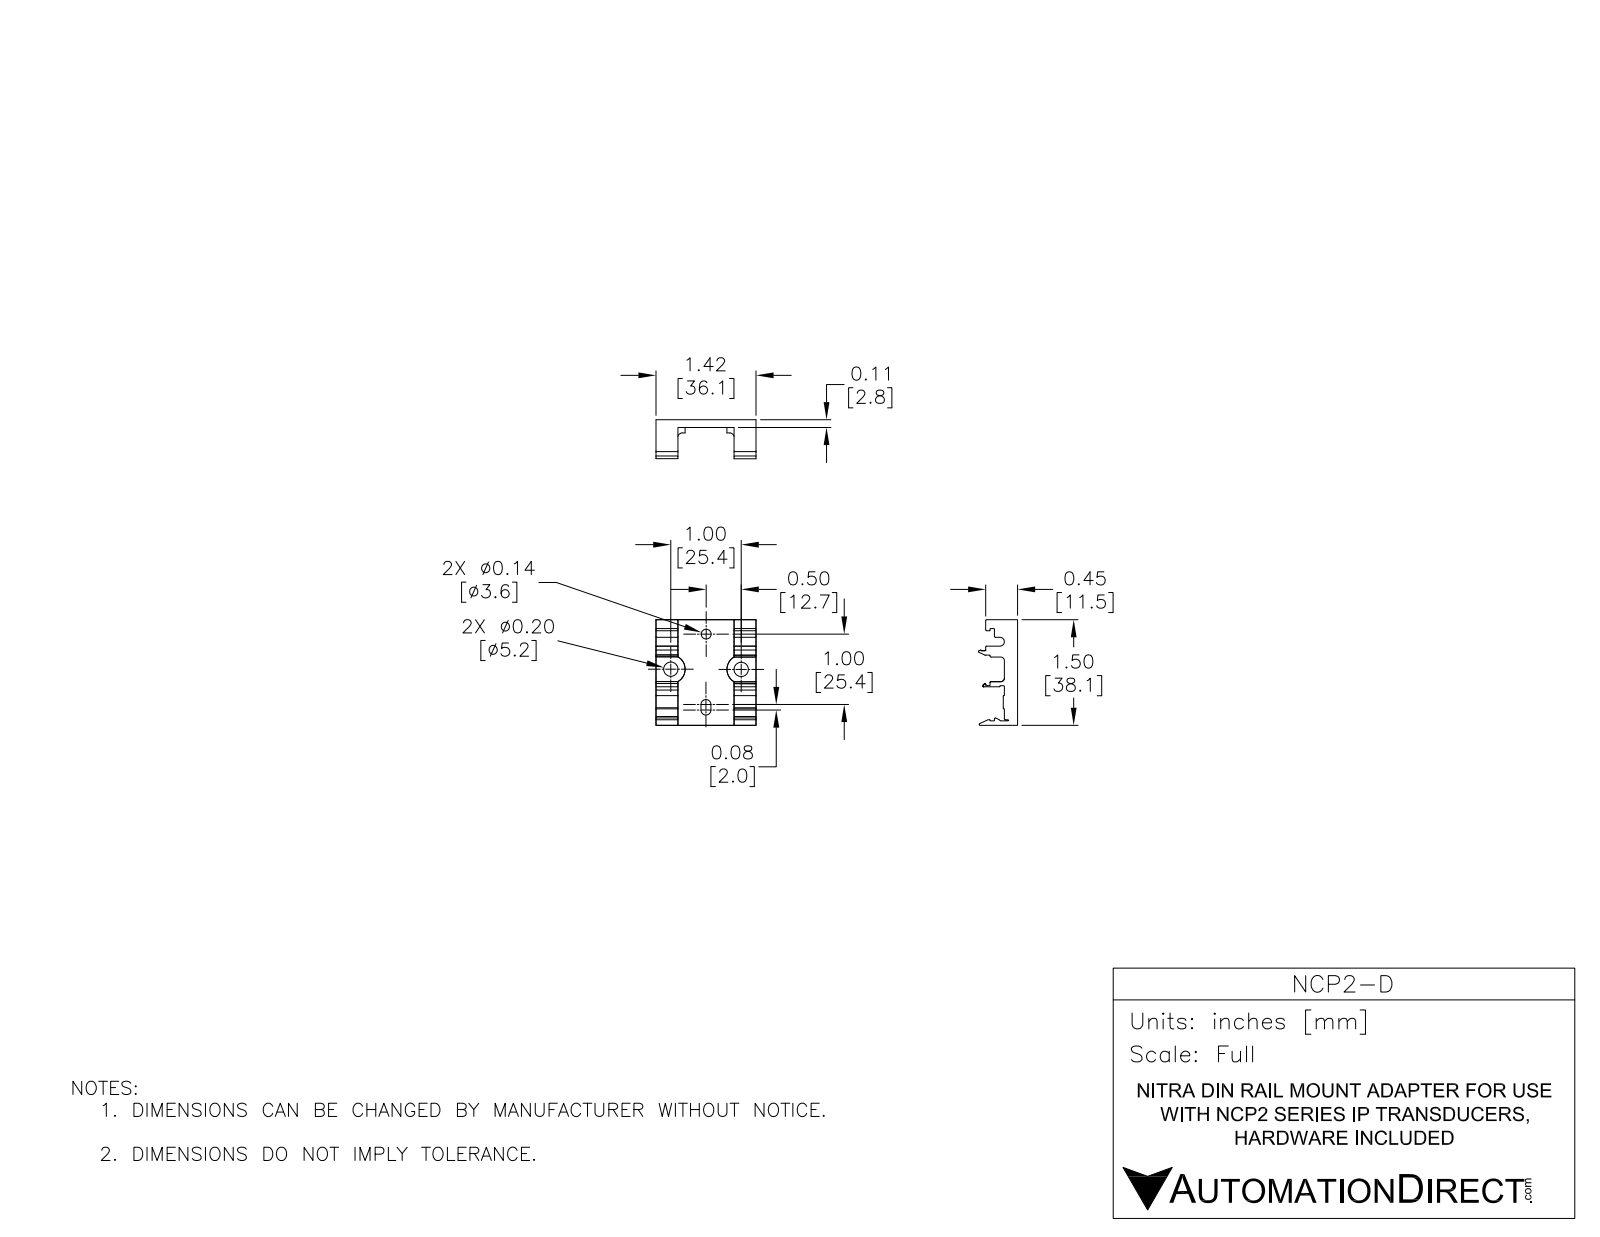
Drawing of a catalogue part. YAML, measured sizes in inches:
part_name: "NCP2-D"
step_written_by: "SolidWorks 2016 (AUTOMOTIVE_DESIGN)"
units: inches
bodies: {solids: 1, faces: 187, planar: 90, cylindrical: 95, other: 2}
overall_size: [1.5, 1.422, 0.555]
volume: 0.382
surface_area: 7.861
round_holes:
  - {diameter: 0.203, count: 2}
  - {diameter: 0.141, count: 1}
partial_cylinders:
  - {radius: 0.007, count: 17}
  - {radius: 0.012, count: 10}
  - {radius: 0.013, count: 10}
  - {radius: 0.05, count: 4}
  - {radius: 0.07, count: 2}
  - {radius: 0.203, count: 2}
  - {radius: 0.062, count: 1}
face_to_face_distances: [0.109, 0.313, 1.109, 1.422, 1.5, 0.187, 0.078, 0.797, 0.063, 0.25]
hole_center_spacings: [0.707, 0.707, 1]
